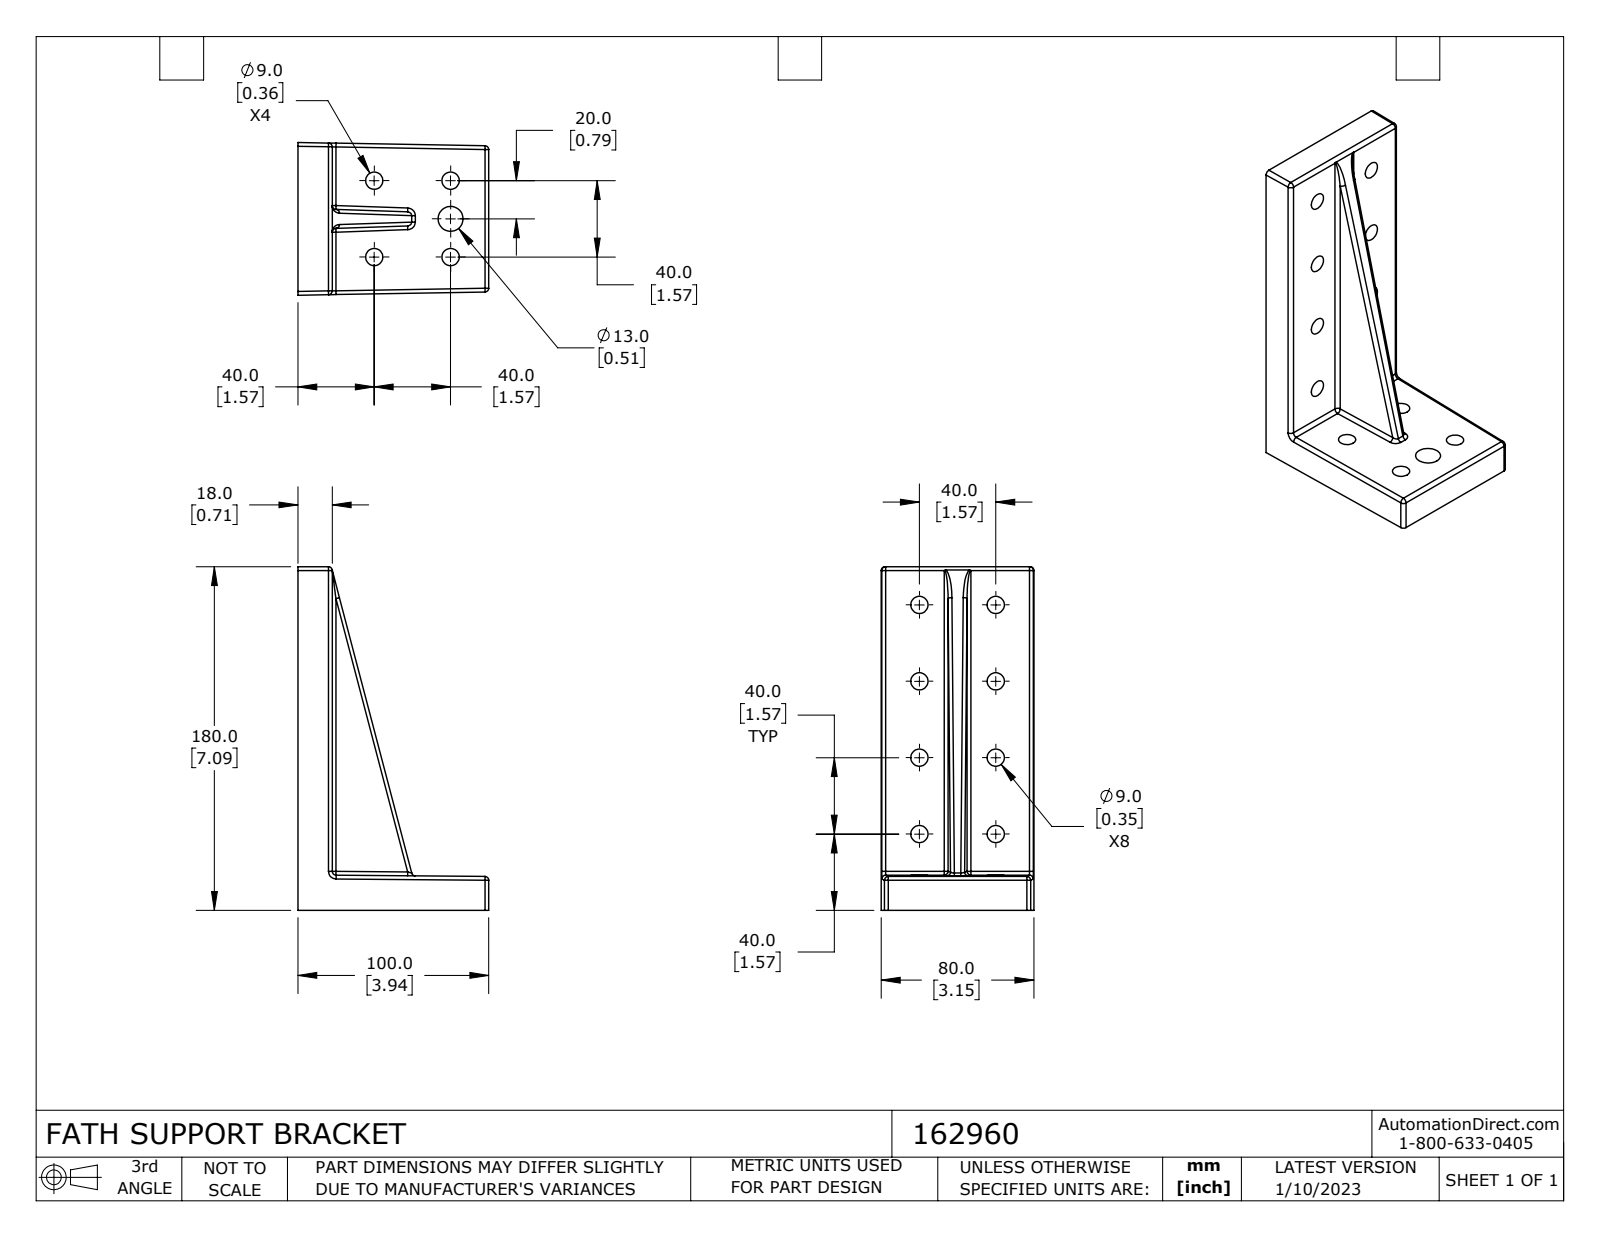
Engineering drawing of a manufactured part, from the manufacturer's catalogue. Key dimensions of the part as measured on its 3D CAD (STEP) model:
Part name (STEP PRODUCT): 162960
STEP written by: SolidWorks 2021 (CONFIG_CONTROL_DESIGN)
Units: inches
Bodies: 1 solid, 418 faces (98 planar, 112 cylindrical, 208 other)
Overall size (bounding box): 7.087 × 3.937 × 3.149
Volume: 15.51 in³ · Surface area: 127.6 in²
Partial cylindrical surfaces — rounded edges, fillets, slot ends (radius × count): R0.02 ×59, R0.079 ×18, R0.039 ×1
Main face-to-face distances: 0.472, 0.236, 0.709, 1.573, 1.114, 3.146, 7.087, 6.614, 3.937, 3.465
